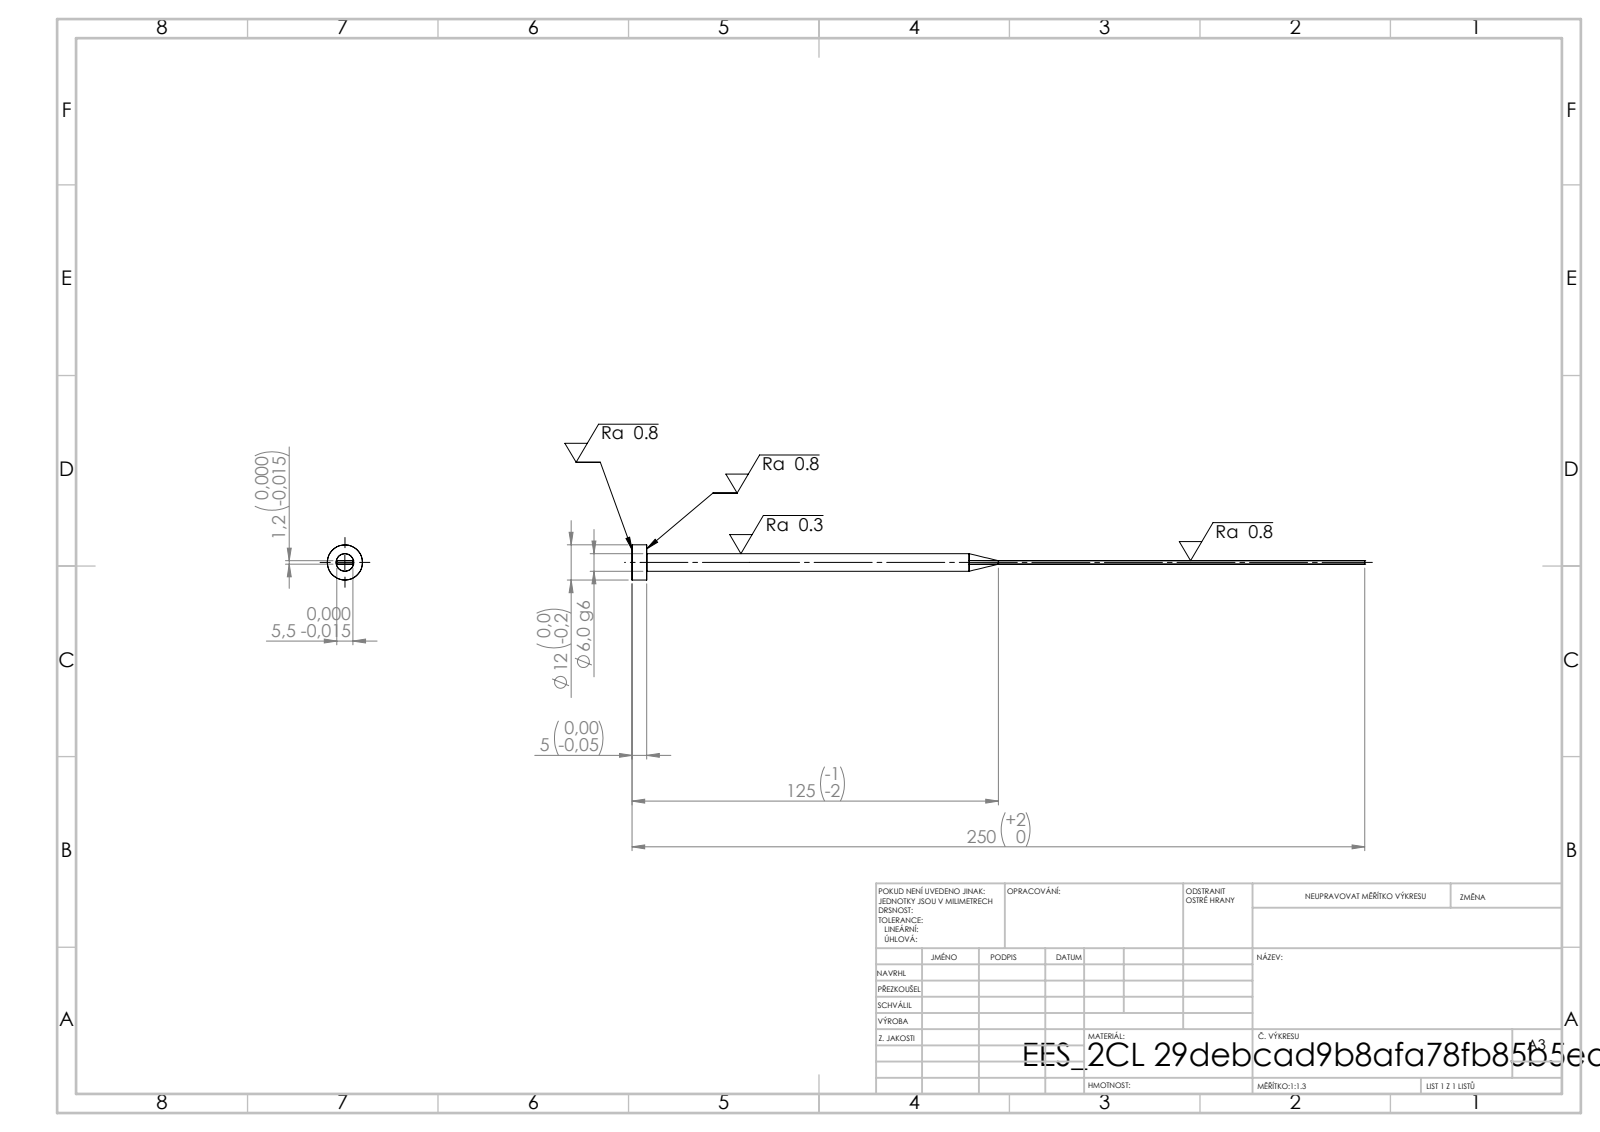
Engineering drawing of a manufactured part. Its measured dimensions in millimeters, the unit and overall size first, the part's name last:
Units: millimetres
Overall size (bounding box): 250 × 12 × 12
Round bosses / shafts (diameter × count): ⌀12 ×1, ⌀6 ×1
Main face-to-face distances: 1.2, 5.5, 5, 250, 245
Volume: 4 666 mm³ · Surface area: 4 298 mm²
Bodies: 1 solid, 15 faces (7 planar, 4 cylindrical, 4 other)
STEP written by: SolidWorks 2019 (CONFIG_CONTROL_DESIGN)
